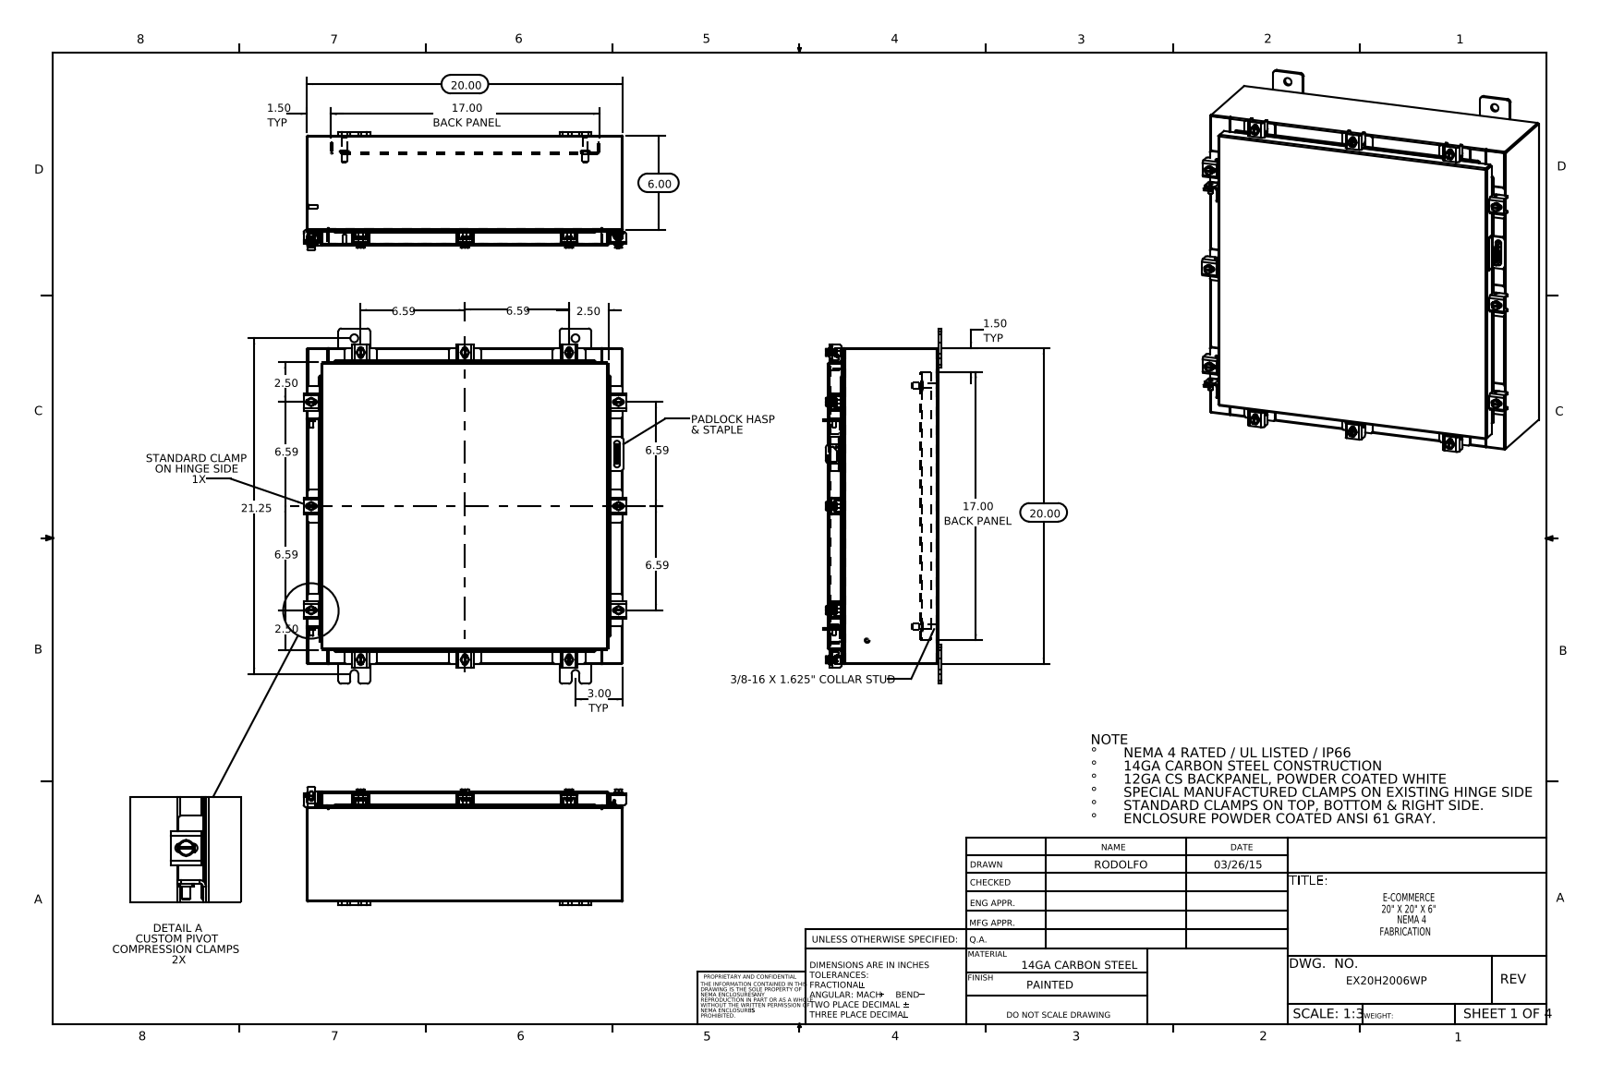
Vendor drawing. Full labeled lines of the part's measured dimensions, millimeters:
Part name (STEP PRODUCT): EX20H2006WP Clamp Bracket; EX20H2006WP Mounting Studs; EX20H2006WP Body; EX20H2006WP Standard Clamps (+8 more)
STEP written by: SolidWorks 2014 (CONFIG_CONTROL_DESIGN)
Units: millimetres
Bodies: 81 solids, 2018 faces (1075 planar, 783 cylindrical, 160 other)
Overall size (bounding box): 571.5 × 518.7 × 189.3
Volume: 2 453 000 mm³ · Surface area: 2 410 000 mm²
Round holes (diameter × count): ⌀5.4 ×12, ⌀6.6 ×12, ⌀12.7 ×8, ⌀3.2 ×1, ⌀6.4 ×1
Round bosses / shafts (diameter × count): ⌀12.7 ×12, ⌀6.4 ×12, ⌀10.1 ×10, ⌀15.9 ×4, ⌀9.5 ×4, ⌀8.4 ×4, ⌀8 ×2, ⌀6 ×2
Partial cylindrical surfaces — rounded edges, fillets, slot ends (radius × count): R1.5 ×54, R0.3 ×24, R3.6 ×24, R4.8 ×24, R2.2 ×22, R3 ×22, R2.3 ×18, R1.3 ×17
Main face-to-face distances: 1.9, 175.3, 506.1, 177.2, 173.4, 2.6, 25.4, 27.3, 148, 149.9
Hole centre spacings: 167.5, 259.5, 422.1, 482.5, 521.7, 59.4, 365.1, 441.5
